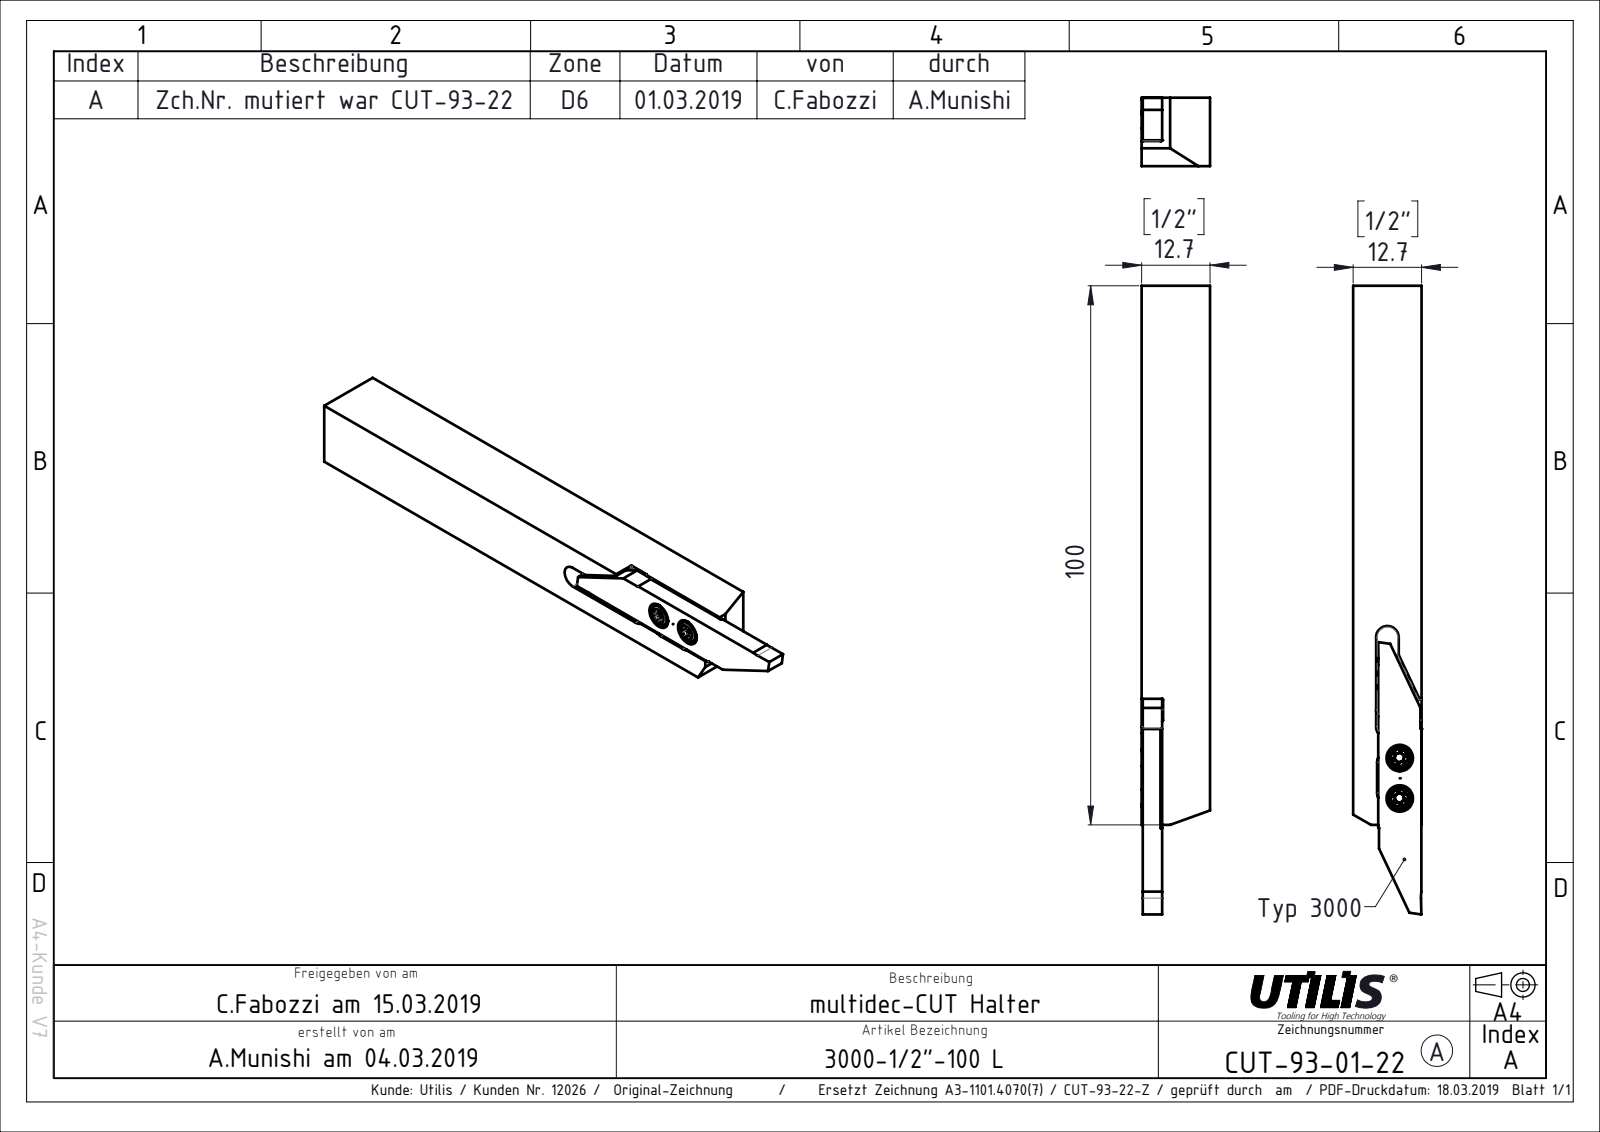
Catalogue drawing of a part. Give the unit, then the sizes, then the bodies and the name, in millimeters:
Units: millimetres
Overall size (bounding box): 116.5 × 12.7 × 12.7
Round holes (diameter × count): ⌀2.5 ×2, ⌀4.9 ×2
Partial cylindrical surfaces — rounded edges, fillets, slot ends (radius × count): R2.1 ×4, R0.15 ×2, R10 ×2
Main face-to-face distances: 12.7, 3.8, 8.9, 3.6, 12.5, 4.7, 8, 4.25, 8.45, 0.45
Hole centre spacings: 3.75, 7.5
Volume: 15 937 mm³ · Surface area: 6 618 mm²
Bodies: 2 solids, 55 faces (36 planar, 19 cylindrical, 0 other)
Part name (STEP PRODUCT): CUT-93-Kunde; CUT-Vorlage 3000 R+L Lang Kunde; CUT-93-22; CUT-Vorlage 3000 R+L Lang Kunde_L-Lang (+1 more)
STEP written by: SolidWorks 2015 (CONFIG_CONTROL_DESIGN)
